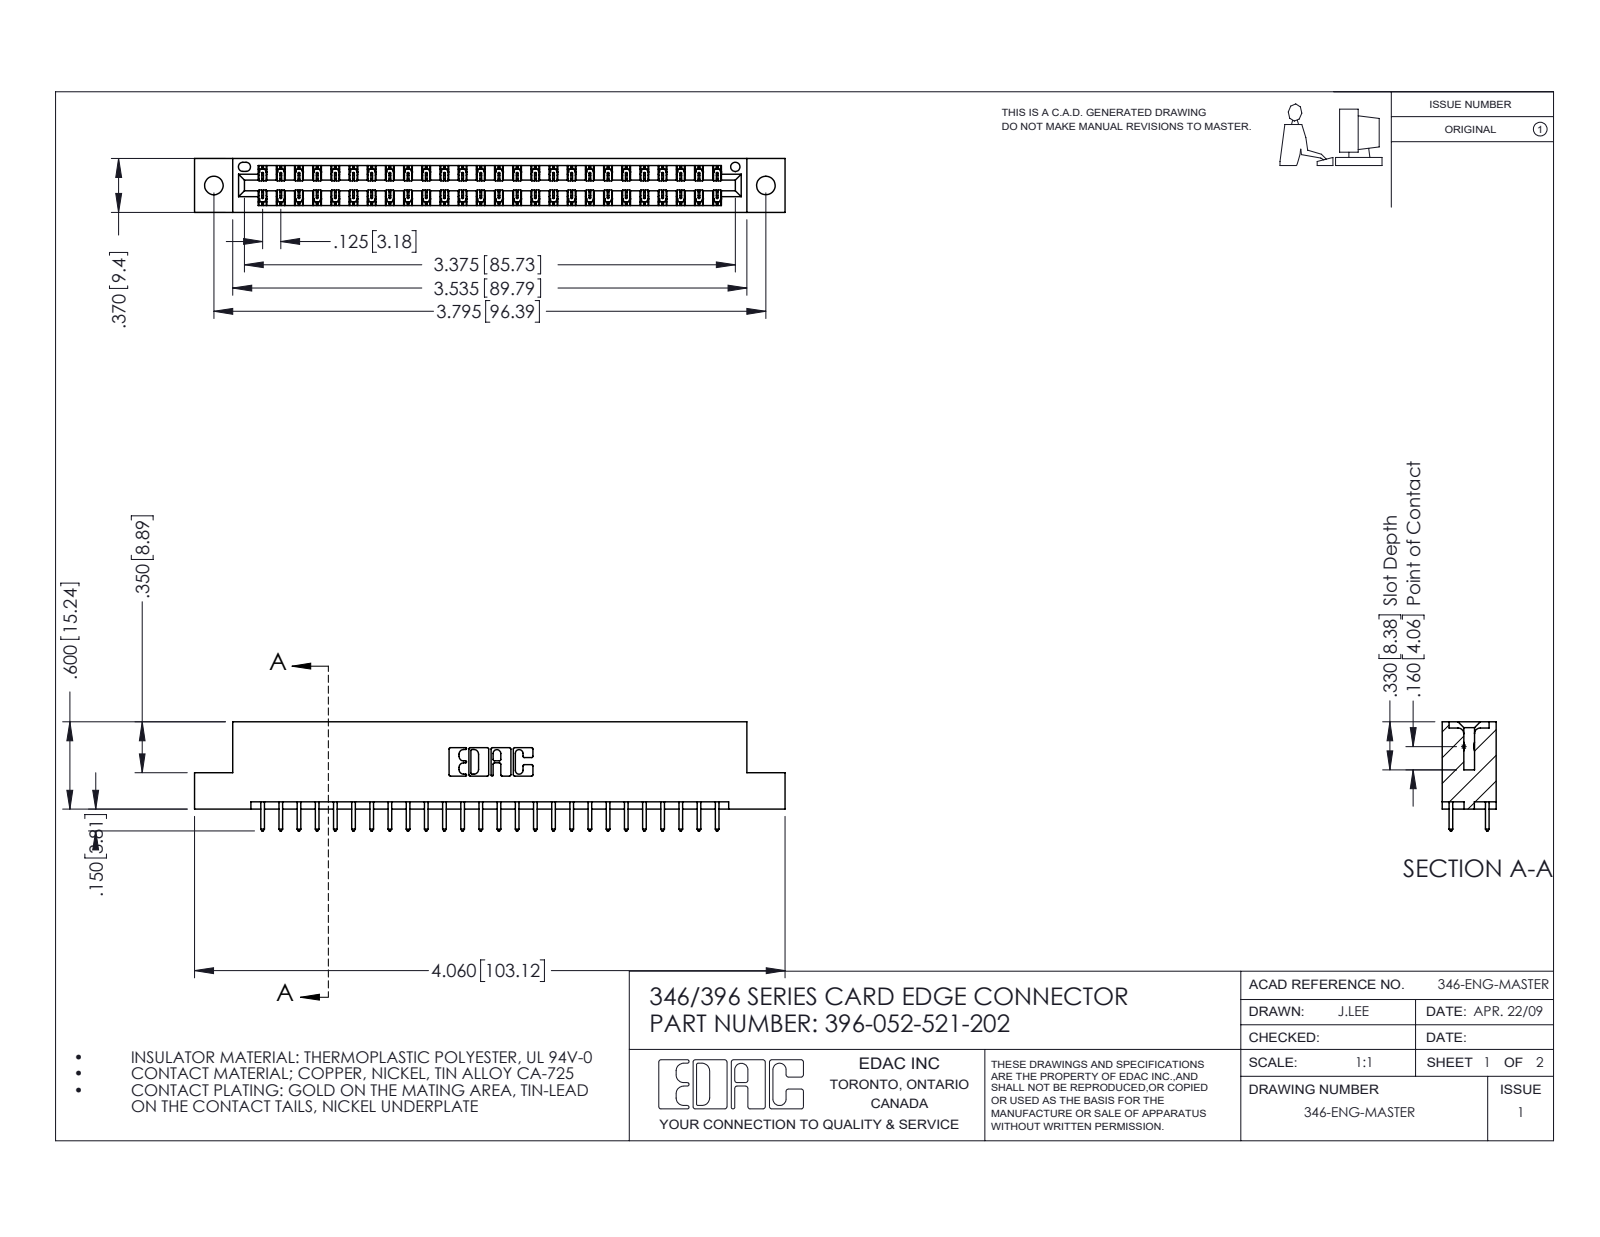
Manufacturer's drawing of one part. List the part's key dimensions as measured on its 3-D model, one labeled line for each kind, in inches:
Part name (STEP PRODUCT): 345-292-001_345-293-121; 396-052-521-202; 346 Part_Flush Mounting Lugs - 0.128 Dia
STEP written by: SolidWorks 2016 (CONFIG_CONTROL_DESIGN)
Units: inches
Bodies: 53 solids, 2826 faces (1896 planar, 930 cylindrical, 0 other)
Overall size (bounding box): 4.06 × 0.75 × 0.37
Volume: 0.603 in³ · Surface area: 20.01 in²
Round holes (diameter × count): ⌀0.128 ×2, ⌀0.064 ×1
Partial cylindrical surfaces — rounded edges, fillets, slot ends (radius × count): R0.006 ×78, R0.01 ×52, R0.01 ×22, R0.007 ×6, R0.031 ×6, R0.026 ×3, R0.014 ×2, R0.022 ×2
Main face-to-face distances: 0.048, 0.322, 0.25, 0.37, 0.072, 0.298, 0.025, 0.275, 0.148, 0.222
Hole centre spacings: 0.246, 3.587, 3.795
